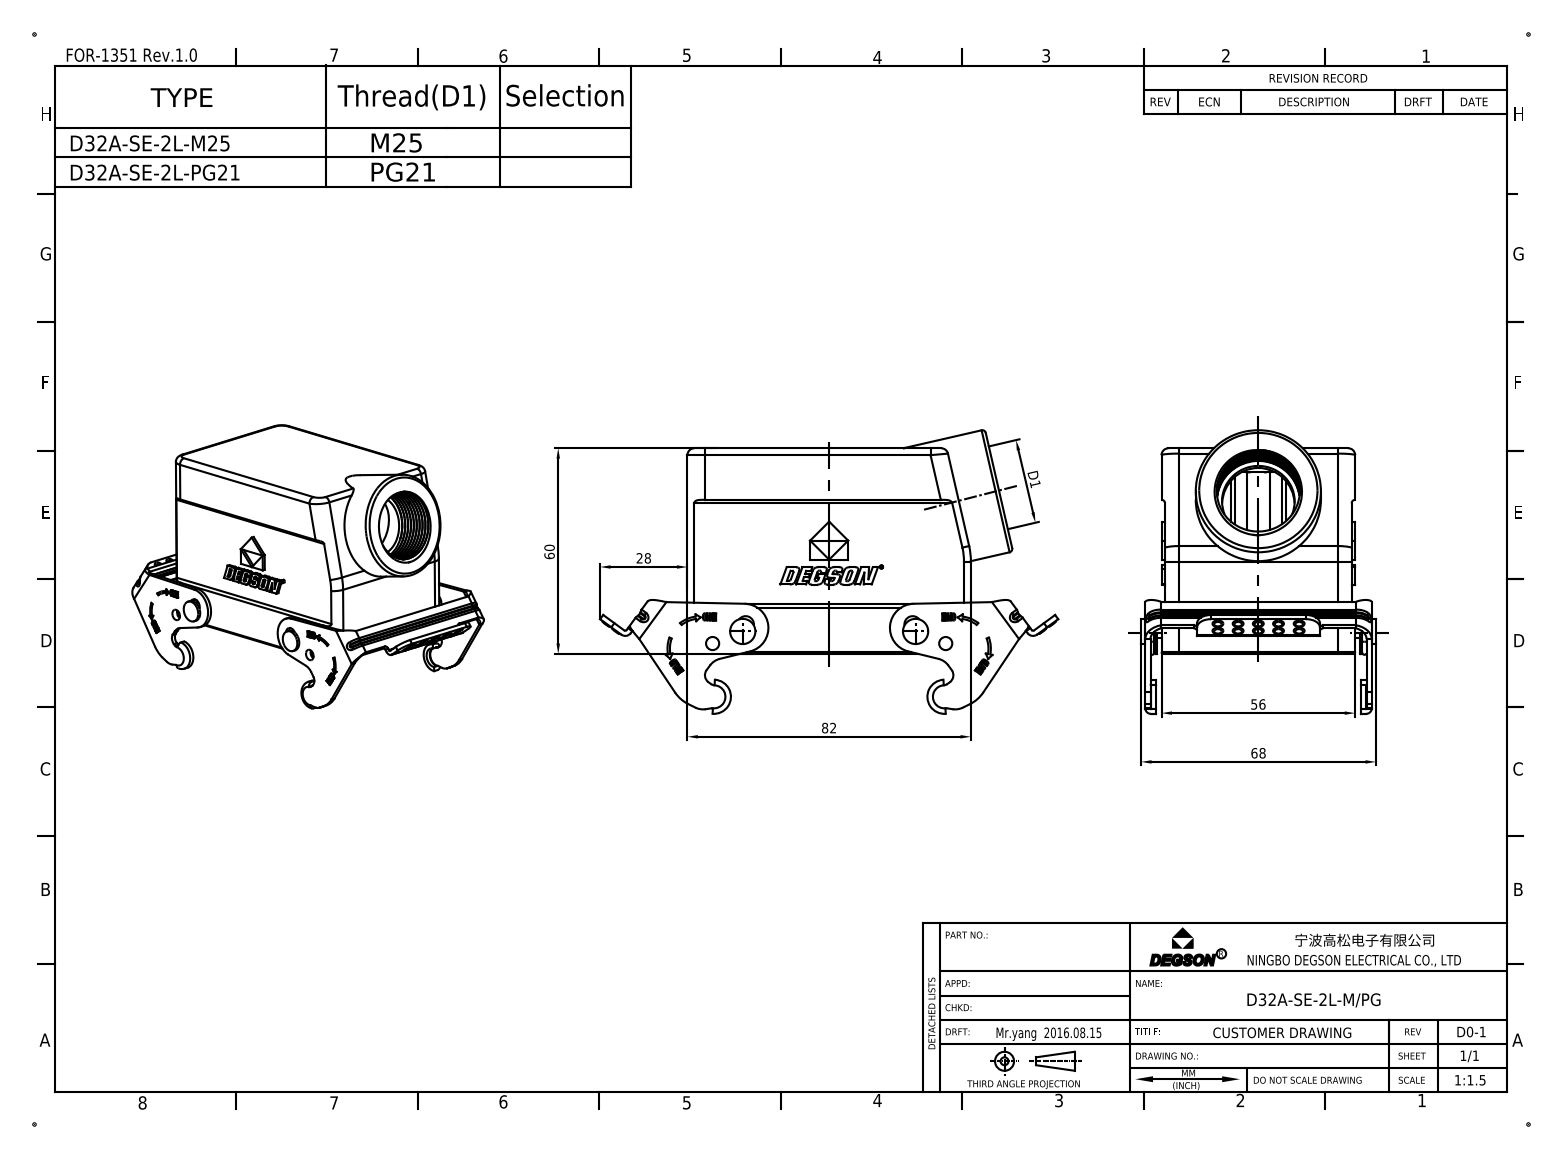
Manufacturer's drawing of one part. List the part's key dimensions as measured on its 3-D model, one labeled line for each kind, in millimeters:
Part name (STEP PRODUCT): D32A-SE-2L-MPG
STEP written by: CREO PARAMETRIC BY PTC INC, 2018100 (CONFIG_CONTROL_DESIGN)
Units: millimetres
Bodies: 2 solids, 392 faces (130 planar, 130 cylindrical, 132 other)
Overall size (bounding box): 132.49 × 80.56 × 67.8
Volume: 92 216 mm³ · Surface area: 51 415 mm²
Round holes (diameter × count): ⌀2.8 ×8, ⌀21 ×1, ⌀24 ×1
Round bosses / shafts (diameter × count): ⌀7.3 ×2, ⌀3.5 ×2, ⌀6 ×1, ⌀4 ×1
Partial cylindrical surfaces — rounded edges, fillets, slot ends (radius × count): R2 ×12, R5 ×10, R1 ×8, R0.5 ×6, R2.5 ×4, R3 ×4, R4 ×4, R4.5 ×4
Main face-to-face distances: 3, 2, 52, 1, 50, 53, 55, 10.5, 1.5, 64
Hole centre spacings: 16, 24, 66, 67.91, 70.23, 8, 40, 66.48
